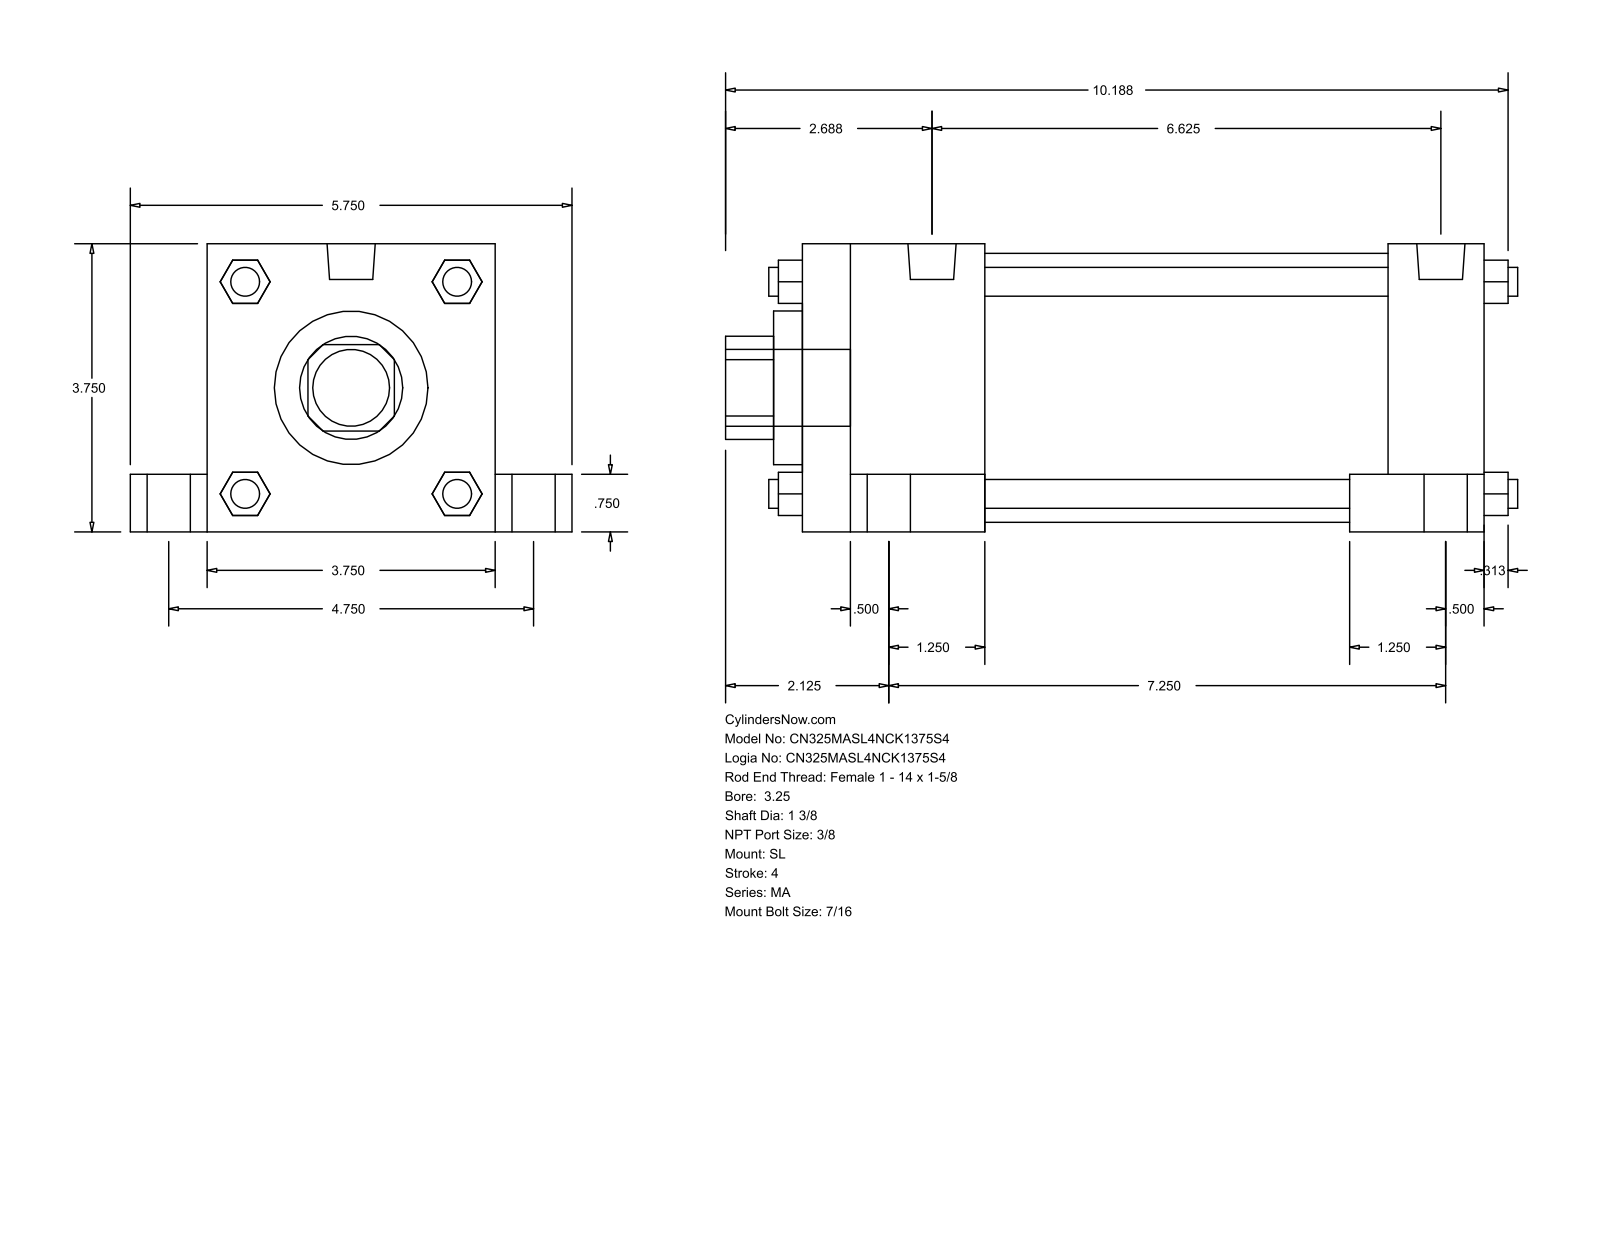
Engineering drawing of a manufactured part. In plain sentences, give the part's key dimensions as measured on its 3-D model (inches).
The part is named "MA_SL__0325_1.375". Its 3-D file was written by "GSSL Pune (CONFIG_CONTROL_DESIGN)". It is 0 solids with 148 faces: 112 planar, 36 cylindrical and 0 other. Overall it measures 10.313 by 5.75 by 3.75 inches. Round holes: 1 of diameter 1.375, 1 of diameter 2, 1 of diameter 3.5. Round bosses or shafts: 4 of diameter 0.813, 4 of diameter 0.563, 4 of diameter 0.437, 4 of diameter 0.375, 2 of diameter 0.627, 1 of diameter 1. Partial cylindrical surfaces (rounded edges, fillets, slot ends): 1 of radius 0.672. The main face-to-face distances are 3.75, 8.875, 5.25, 1, 4.75, 7.625, 1.25, 2.375, 6.5, 0.75.
